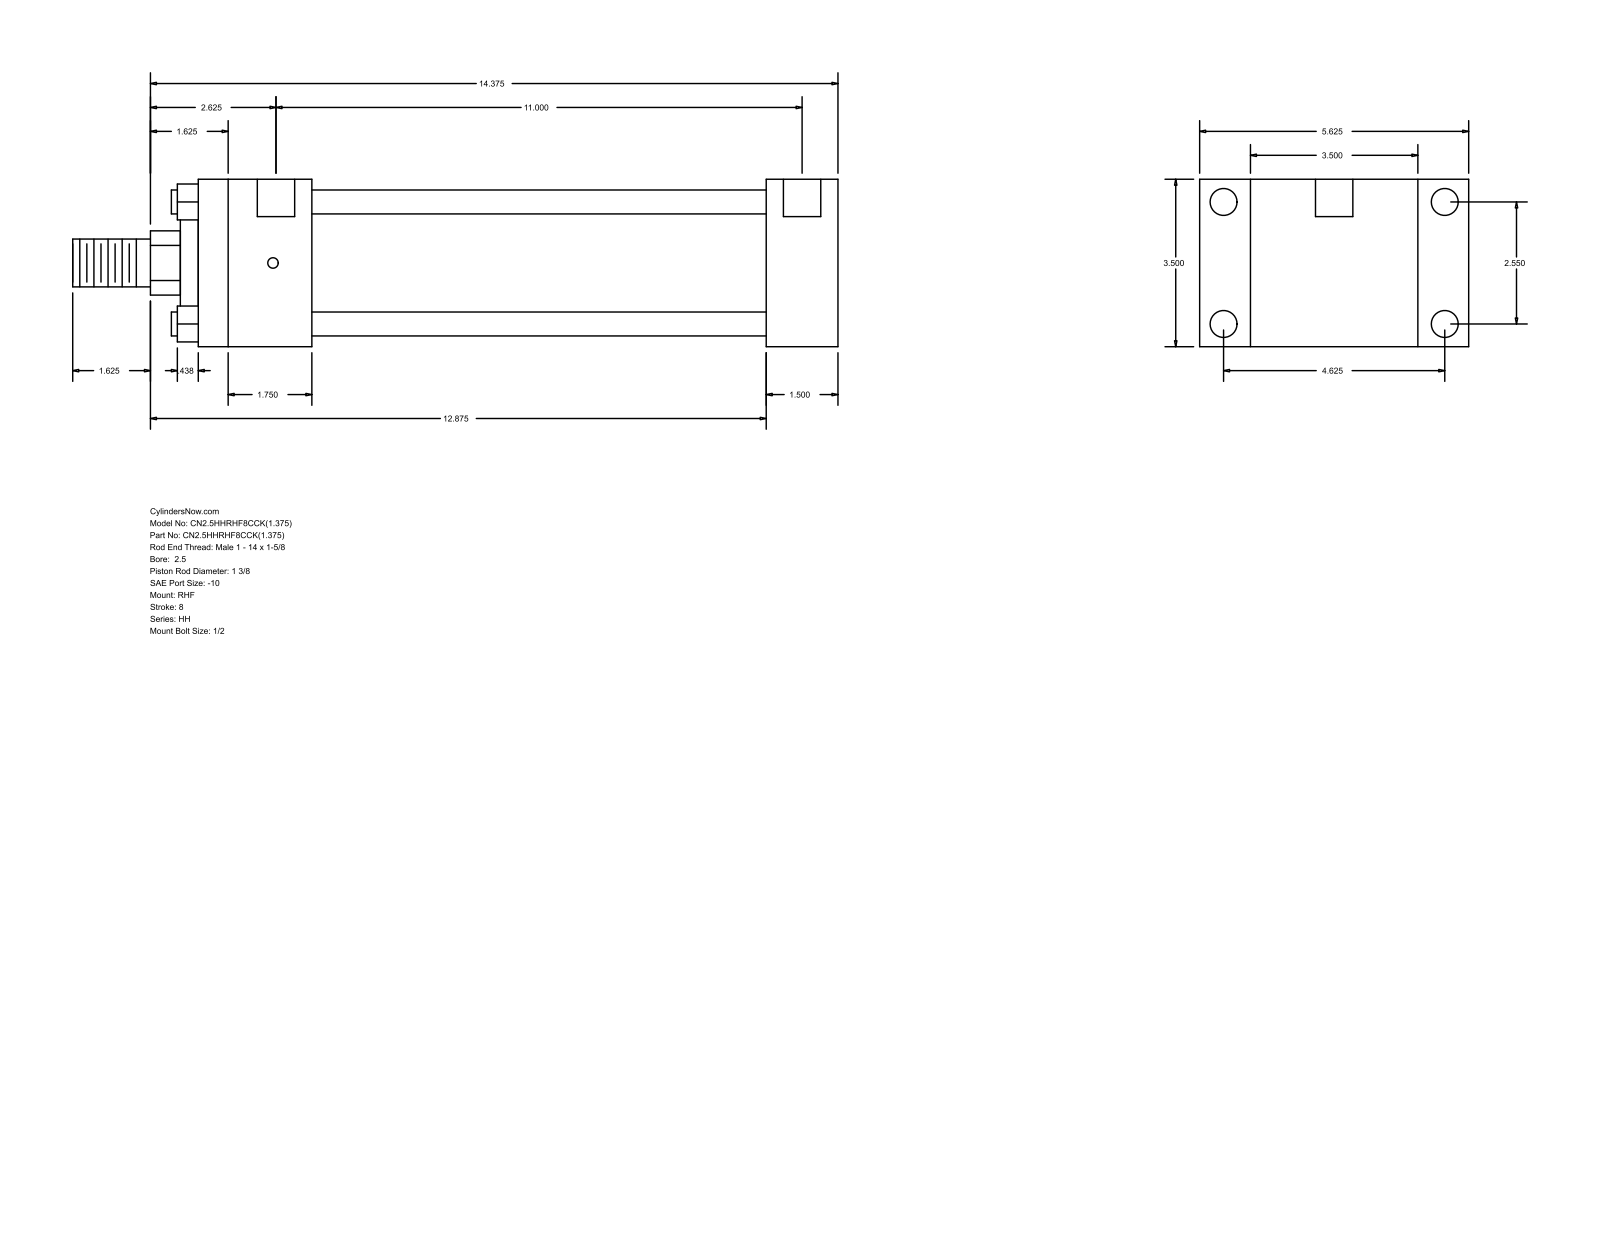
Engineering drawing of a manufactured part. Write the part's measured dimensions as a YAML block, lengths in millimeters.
part_name: "HH_RHF__0250_1.375"
step_written_by: "GSSL Pune (CONFIG_CONTROL_DESIGN)"
units: millimeters
bodies: {solids: 0, faces: 88, planar: 60, cylindrical: 28, other: 0}
overall_size: [406.4, 142.88, 88.9]
round_holes:
  - {diameter: 5.56, count: 4}
  - {diameter: 14.3, count: 4}
  - {diameter: 19.84, count: 2}
round_bosses_or_shafts:
  - {diameter: 12.7, count: 4}
  - {diameter: 73.03, count: 1}
  - {diameter: 50.8, count: 1}
  - {diameter: 34.92, count: 1}
  - {diameter: 25.4, count: 1}
partial_cylinders:
  - {radius: 17.06, count: 1}
face_to_face_distances: [88.9, 38.1, 26.99, 115.89, 301.62, 339.72, 142.88, 60.32, 241.3, 279.4]
hole_center_spacings: [64.76, 117.48, 134.15, 282.57, 1.58, 1.59, 279.4, 280.98]
